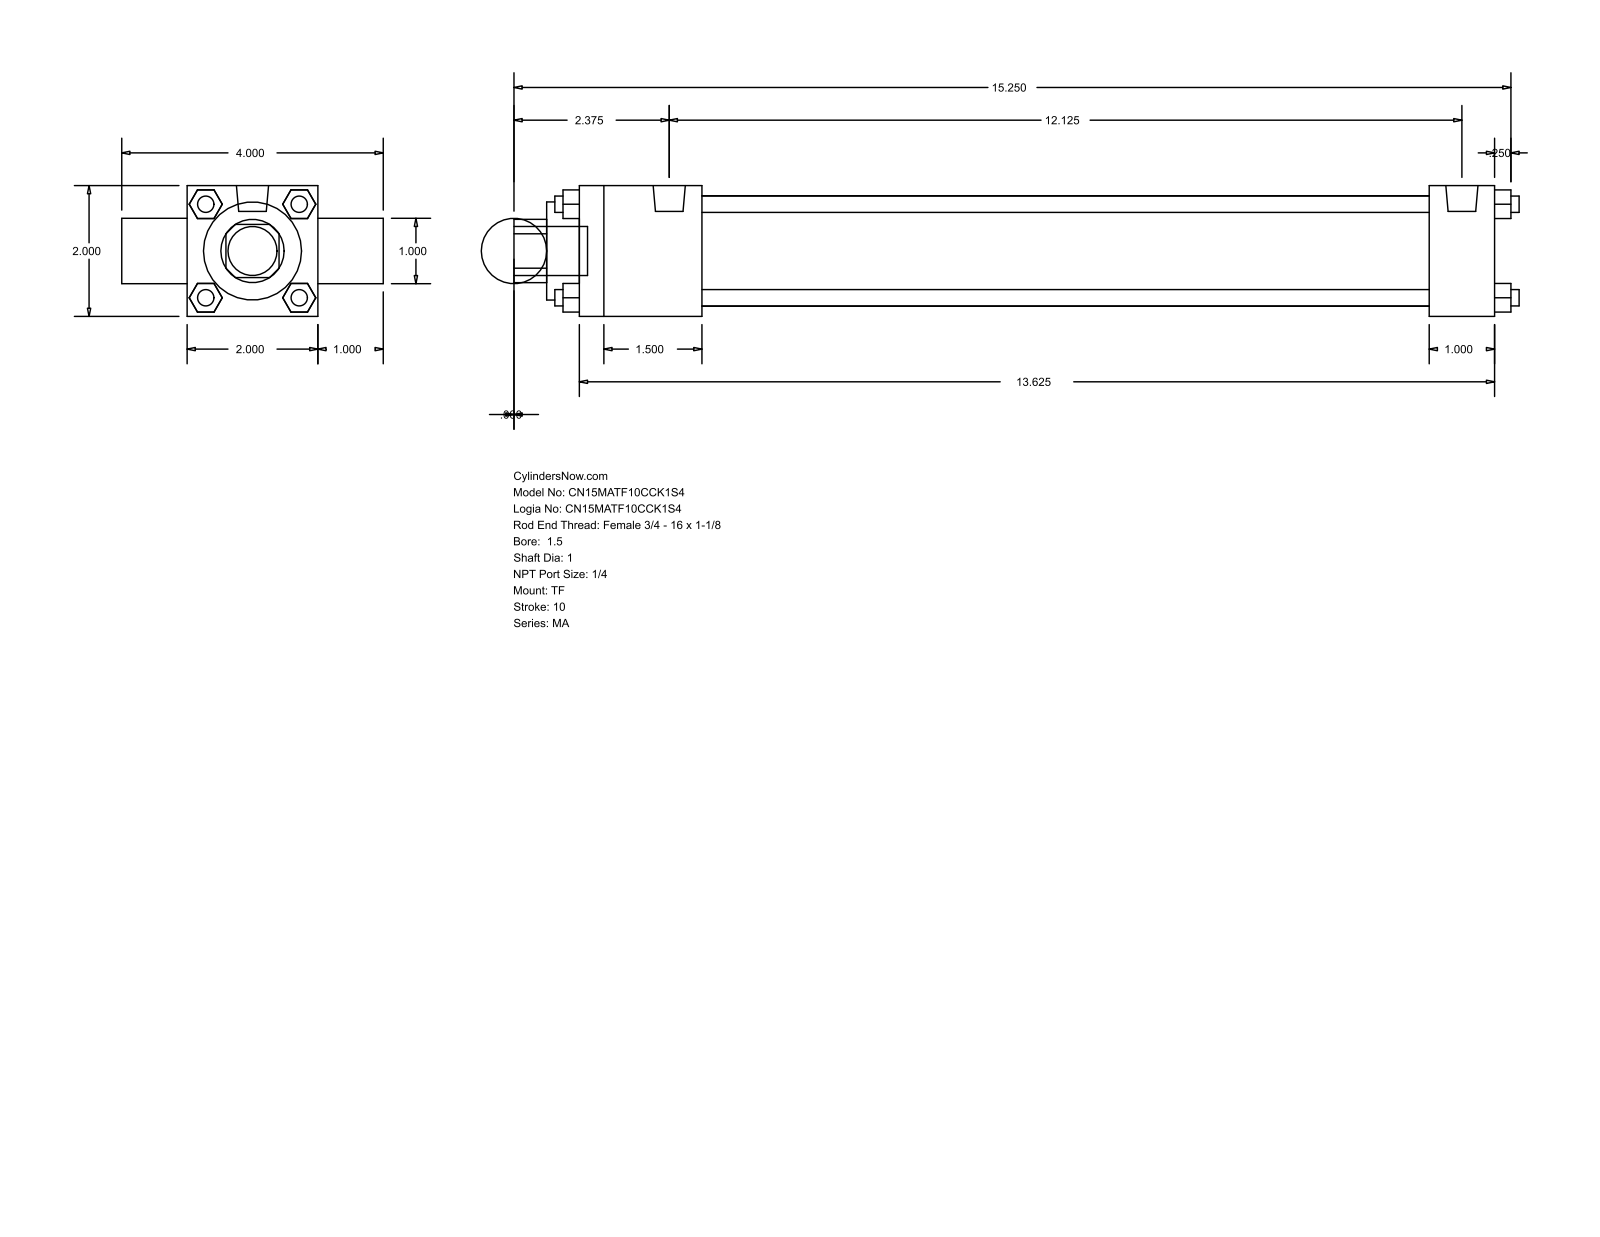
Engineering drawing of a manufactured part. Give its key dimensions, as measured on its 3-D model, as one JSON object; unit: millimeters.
{"part_name": "MA_TF__0150_1", "step_written_by": "GSSL Pune (CONFIG_CONTROL_DESIGN)", "units": "millimeters", "bodies": {"solids": 0, "faces": 120, "planar": 92, "cylindrical": 28, "other": 0}, "overall_size": [390.52, 101.6, 50.8], "round_holes": [[25.4, 2], [38.1, 1], [42.93, 1]], "round_bosses_or_shafts": [[6.35, 4], [7.94, 3], [12.49, 2], [19.05, 1]], "partial_cylinders_radius": [[12.29, 1]], "face_to_face_distances": [50.8, 25.4, 355.6, 76.2, 6.35, 47.63, 330.2, 282.57, 307.97, 368.3]}
